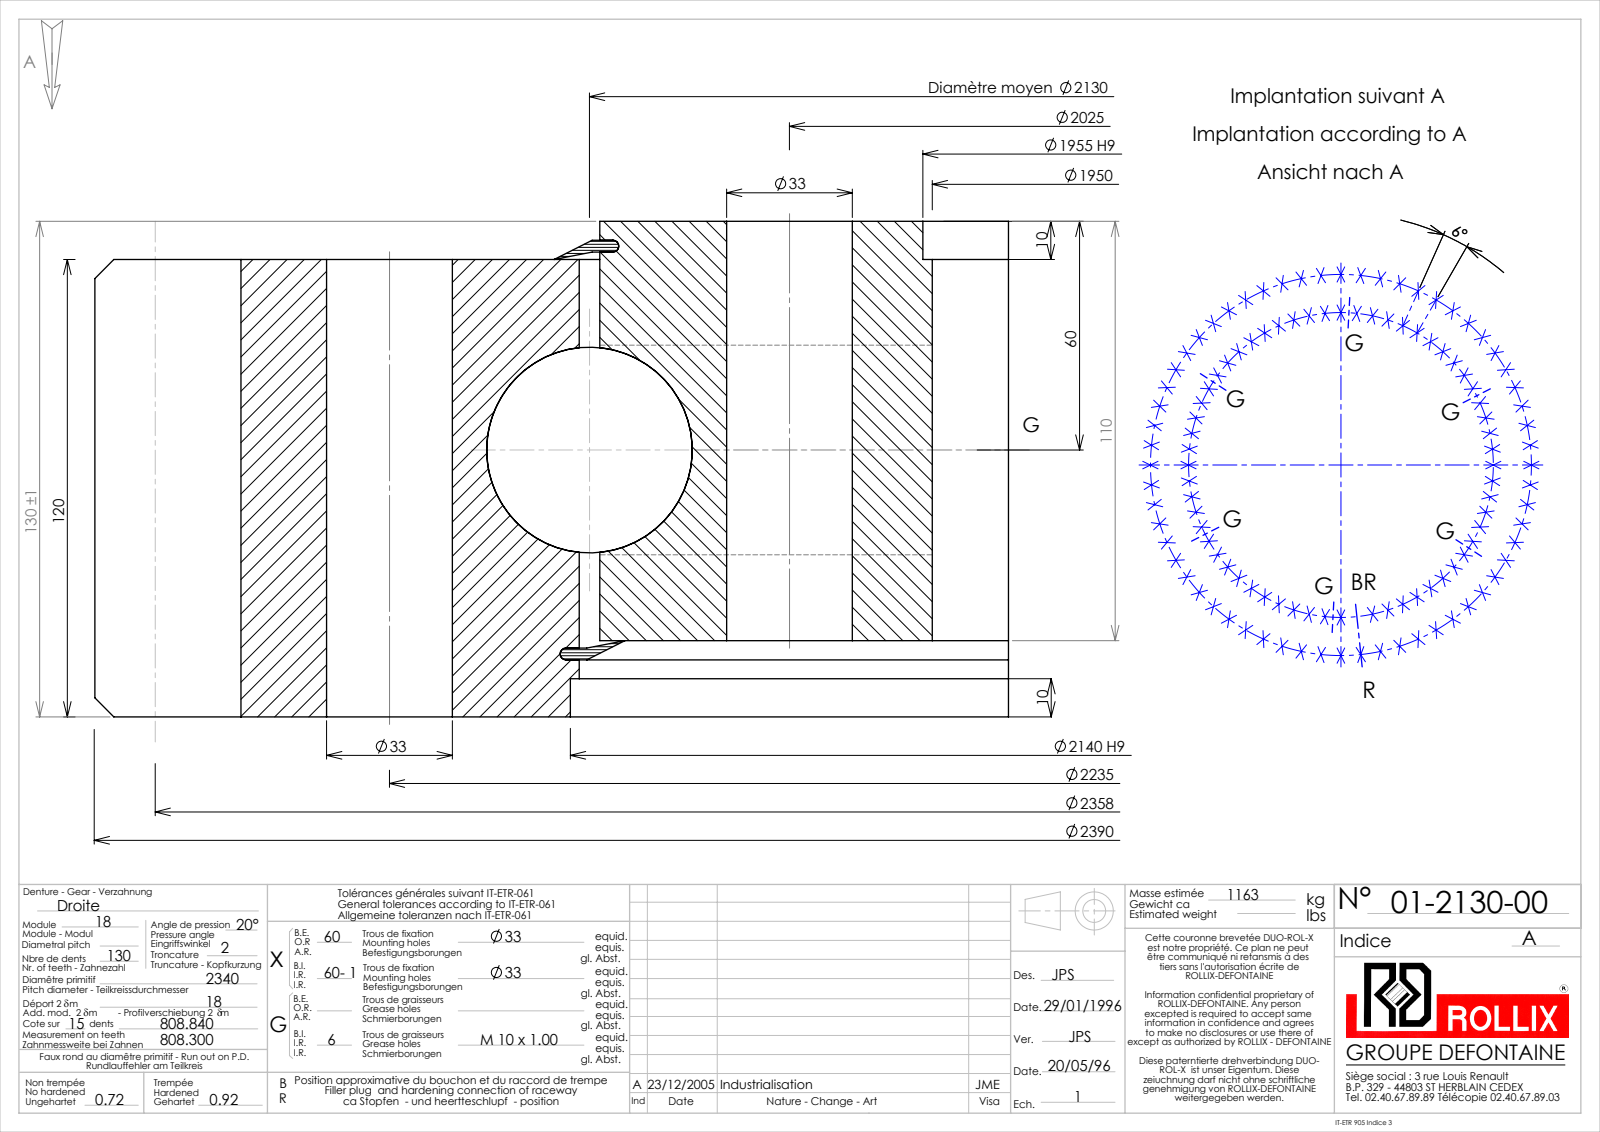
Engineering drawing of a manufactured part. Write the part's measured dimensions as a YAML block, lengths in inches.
part_name: "01-2130-00"
step_written_by: "SolidWorks 2016 (CONFIG_CONTROL_DESIGN)"
units: inches
bodies: {solids: 5, faces: 1091, planar: 274, cylindrical: 529, other: 288}
overall_size: [94.094, 94.081, 5.118]
volume: 7890
surface_area: 13620
round_holes:
  - {diameter: 1.299, count: 119}
  - {diameter: 0.354, count: 6}
  - {diameter: 76.772, count: 1}
  - {diameter: 76.969, count: 1}
  - {diameter: 84.071, count: 1}
  - {diameter: 84.252, count: 1}
round_bosses_or_shafts:
  - {diameter: 83.646, count: 1}
partial_cylinders:
  - {radius: 45.531, count: 1}
  - {radius: 47.047, count: 1}
face_to_face_distances: [4.724, 0.394, 4.331, 0.787, 3.937, 5.118, 0.199, 4.136, 0.077, 4.014]
hole_center_spacings: [4.605, 9.198, 13.765, 22.774, 18.294, 39.948, 43.996, 27.191]
